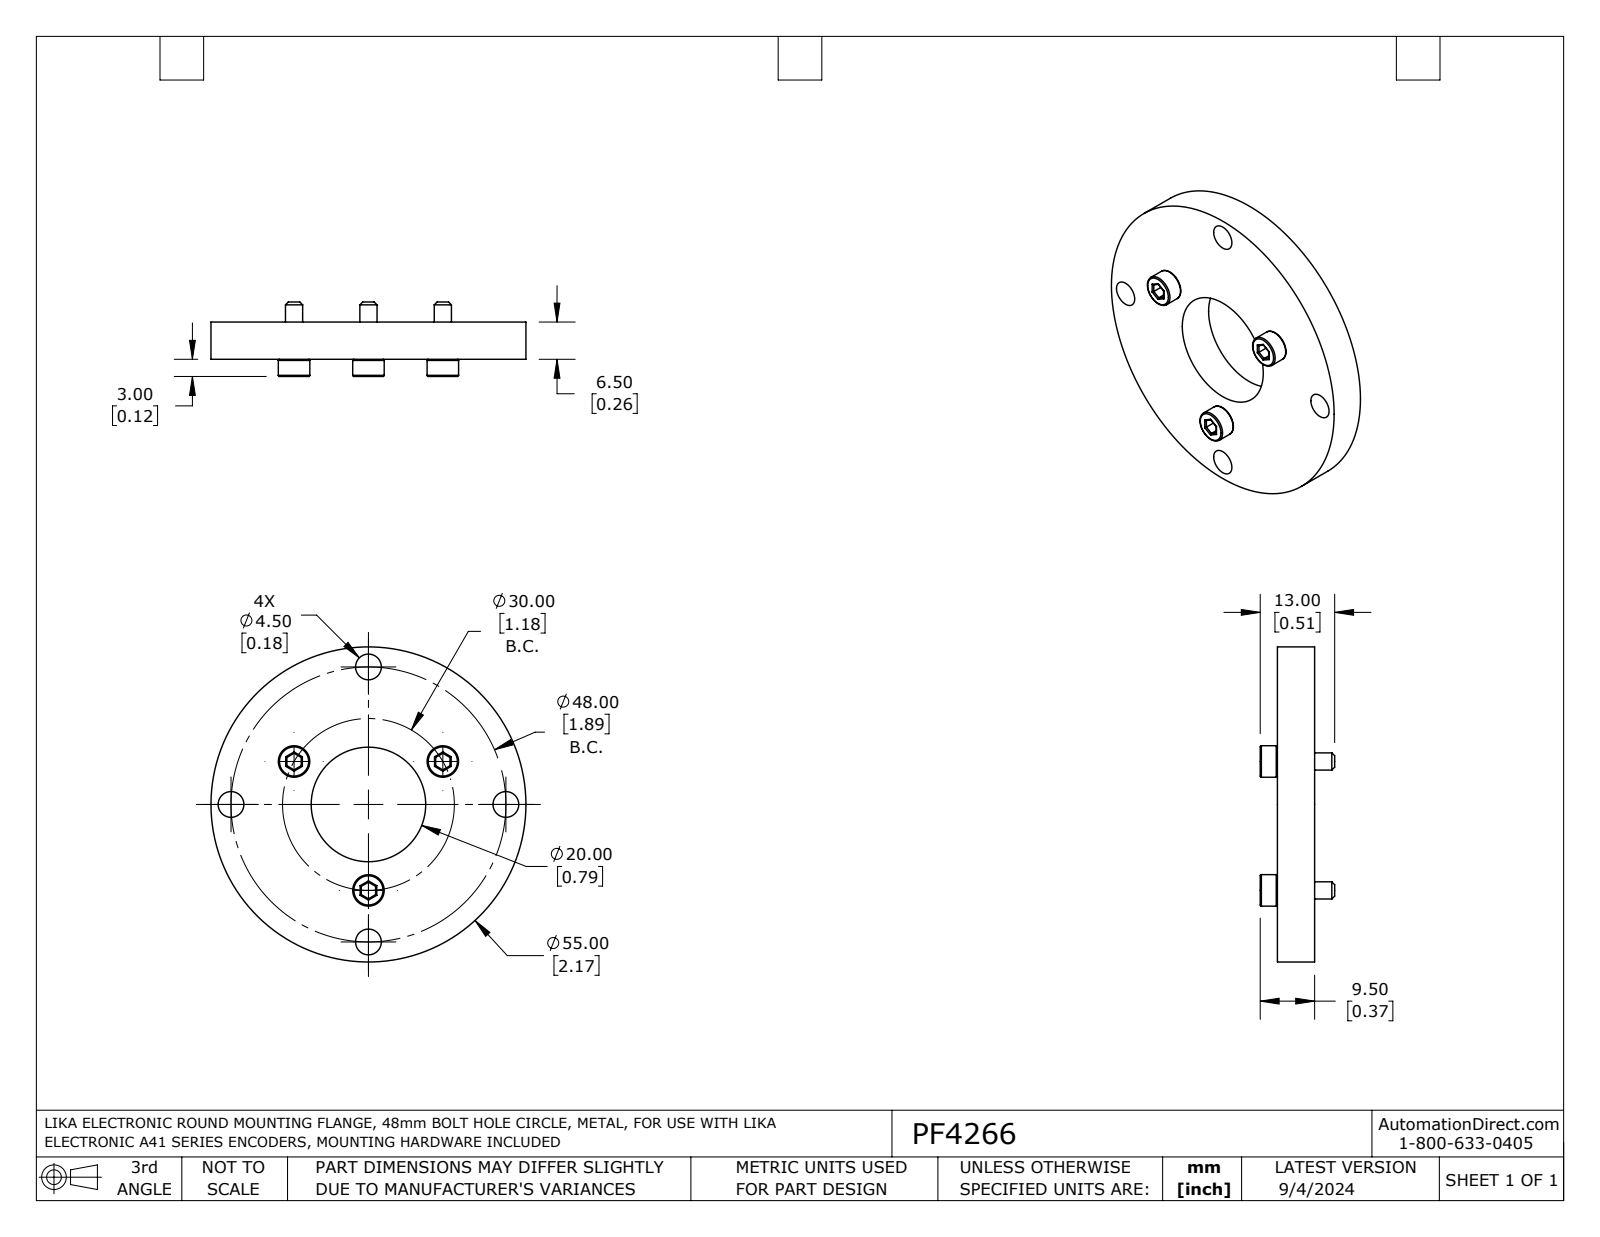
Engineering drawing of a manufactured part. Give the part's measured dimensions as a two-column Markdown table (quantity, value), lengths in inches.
| quantity | value |
| --- | --- |
| part name | PF4266 |
| STEP written by | SolidWorks 2021 (AUTOMOTIVE_DESIGN) |
| units | inches |
| bodies | 4 solids, 98 faces (32 planar, 48 cylindrical, 18 other) |
| overall size | 2.165 × 2.165 × 0.512 |
| volume | 0.805 in³ |
| surface area | 10.33 in² |
| round holes (diameter × count) | 0.177 × 4, 0.138 × 3, 0.787 × 1 |
| round bosses / shafts (diameter × count) | 0.217 × 3, 0.118 × 3, 2.165 × 1 |
| partial cylindrical surfaces (radius × count) | 0.008 × 18 |
| main face-to-face distances | 0.256, 0.374, 0.118, 0.511, 0.098, 0.295, 0.039, 0.079, 1.023, 0.413 |
| hole center spacings | 0.945, 1.336, 0.591, 1.023, 0.524, 0.827, 1.114, 1.341 |
